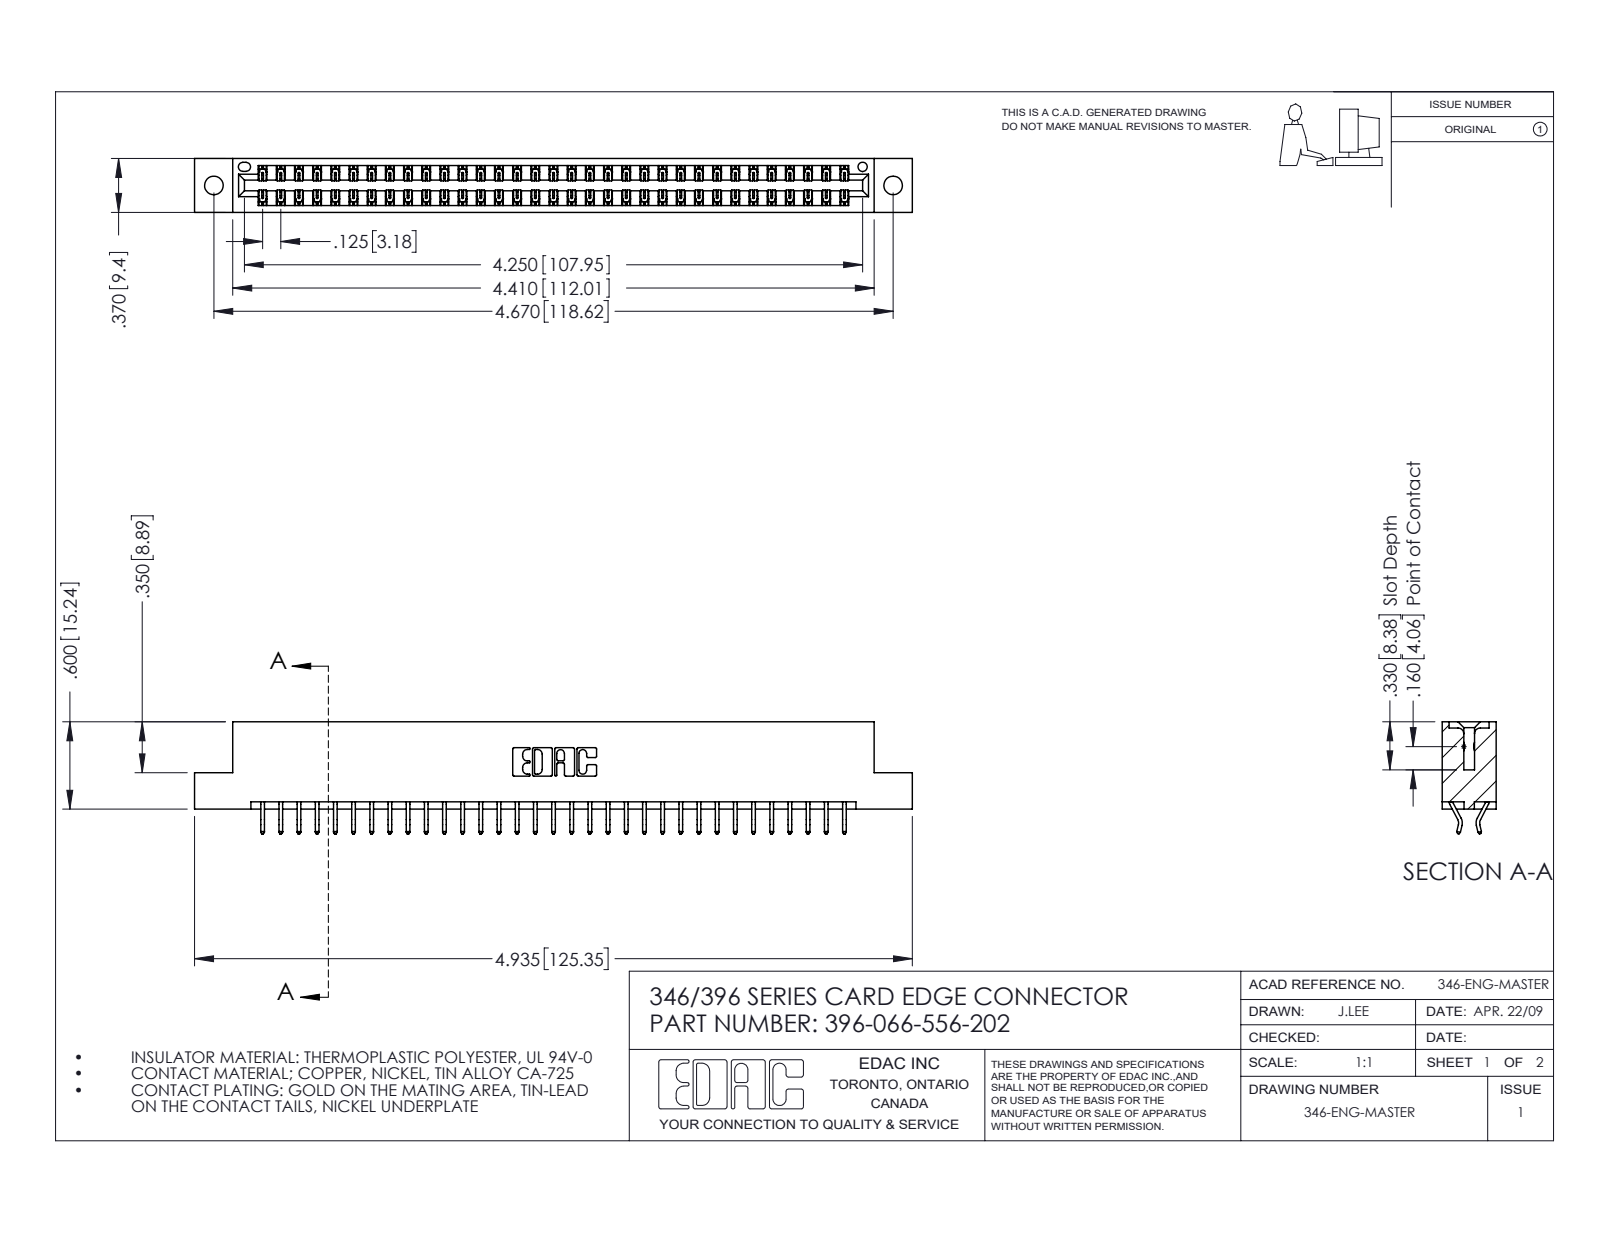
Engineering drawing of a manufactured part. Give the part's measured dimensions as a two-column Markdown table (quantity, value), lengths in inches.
| quantity | value |
| --- | --- |
| part name | 345-292-001_556 Tail; 346 Part_Flush Mounting Lugs - 0.128 Dia; 396-066-556-202 |
| STEP written by | SolidWorks 2016 (CONFIG_CONTROL_DESIGN) |
| units | inches |
| bodies | 67 solids, 3950 faces (2650 planar, 1300 cylindrical, 0 other) |
| overall size | 4.935 × 0.77 × 0.37 |
| volume | 0.739 in³ |
| surface area | 25.08 in² |
| round holes (diameter × count) | 0.128 × 2, 0.064 × 1 |
| partial cylindrical surfaces (radius × count) | 0.006 × 99, 0.01 × 22, 0.007 × 6, 0.031 × 6, 0.026 × 3, 0.01 × 2, 0.014 × 2, 0.022 × 2 |
| main face-to-face distances | 0.048, 0.322, 0.37, 0.25, 0.025, 0.072, 0.298, 0.275, 0.148, 0.222 |
| hole center spacings | 0.246, 4.462, 4.67 |
